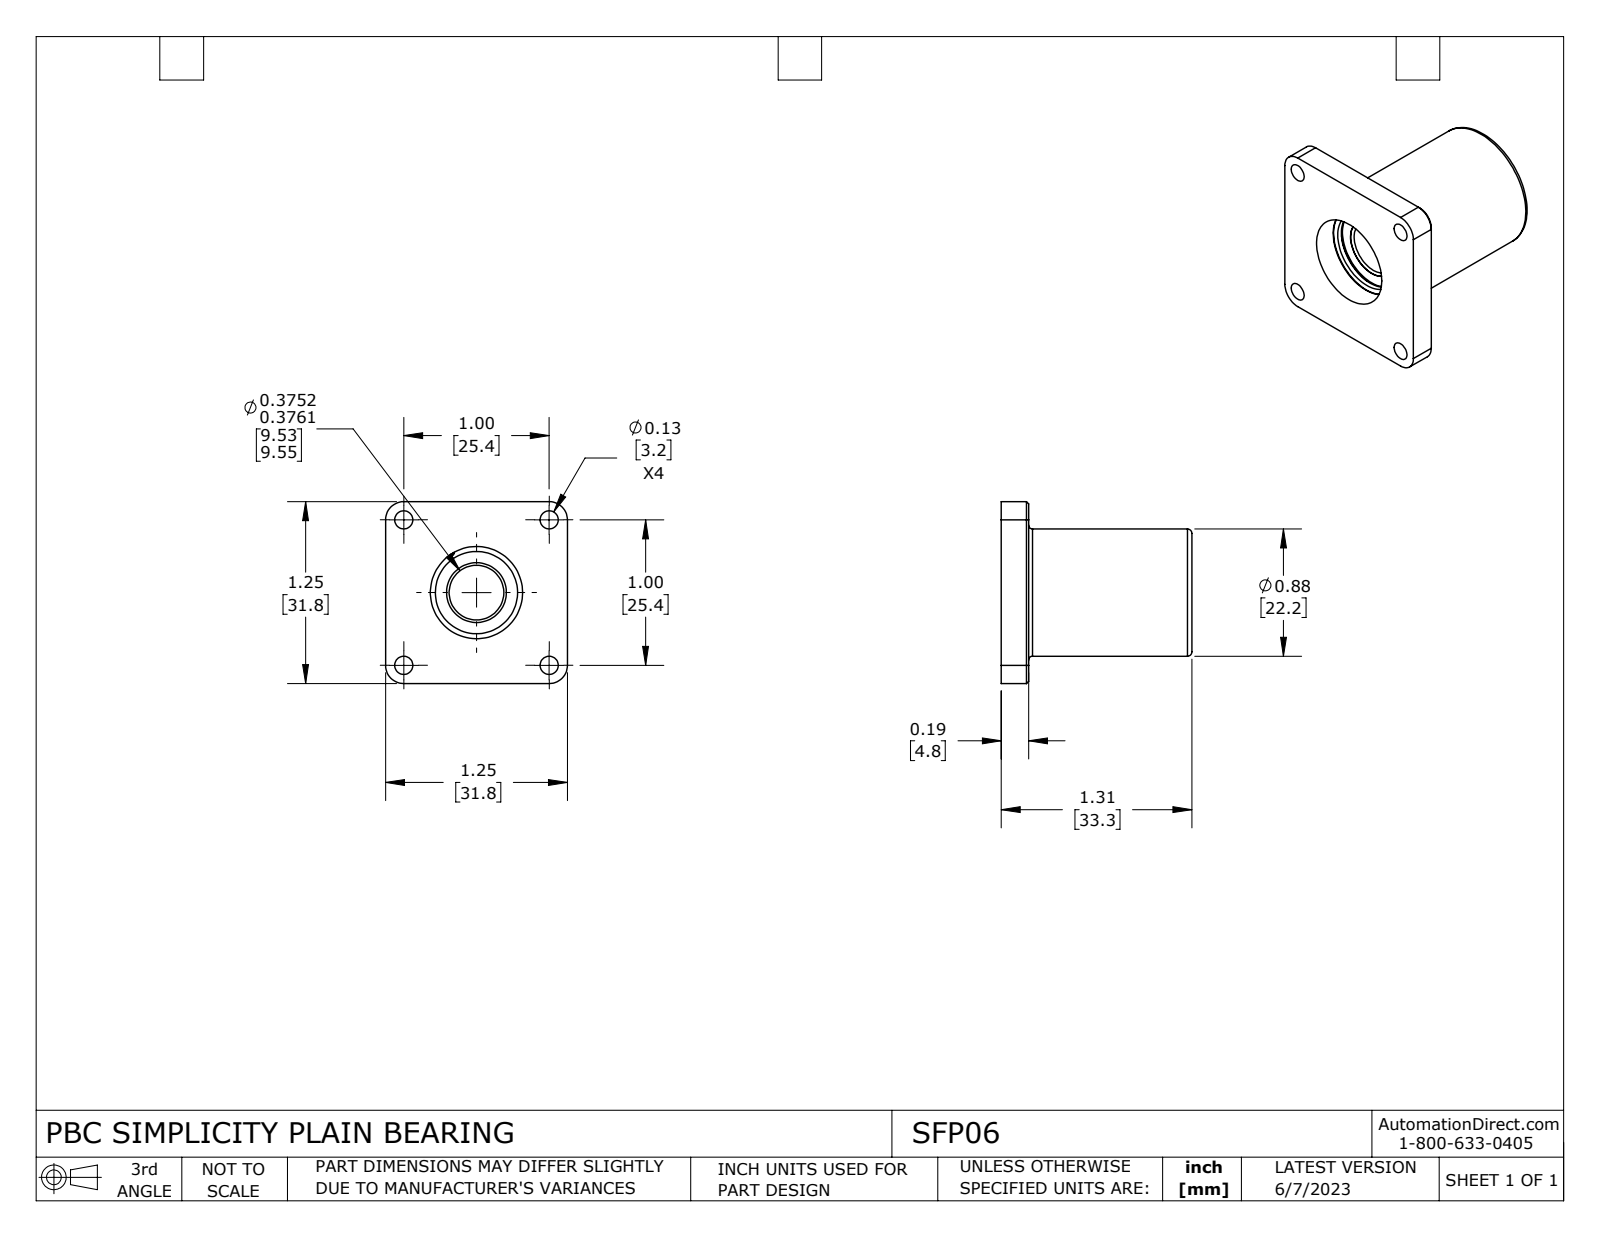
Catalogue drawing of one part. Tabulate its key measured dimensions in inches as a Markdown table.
| quantity | value |
| --- | --- |
| part name | SFP06 |
| STEP written by | SolidWorks 2021 (CONFIG_CONTROL_DESIGN) |
| units | inches |
| bodies | 7 solids, 169 faces (41 planar, 74 cylindrical, 54 other) |
| overall size | 1.31 × 1.25 × 1.25 |
| volume | 0.712 in³ |
| surface area | 16.4 in² |
| round holes (diameter × count) | 0.125 × 4, 0.376 × 1, 0.411 × 1, 0.565 × 1, 0.634 × 1, 0.667 × 1 |
| round bosses / shafts (diameter × count) | 0.875 × 1, 0.675 × 1, 0.624 × 1, 0.587 × 1, 0.524 × 1 |
| partial cylindrical surfaces (radius × count) | 0.009 × 4, 0.125 × 4, 0.004 × 2, 0.014 × 2 |
| main face-to-face distances | 0.188, 1.25, 0.035, 0.931, 1.31, 1.122, 0.26, 0.34, 0.527, 0.607 |
| hole center spacings | 0.707, 1, 1.414 |
